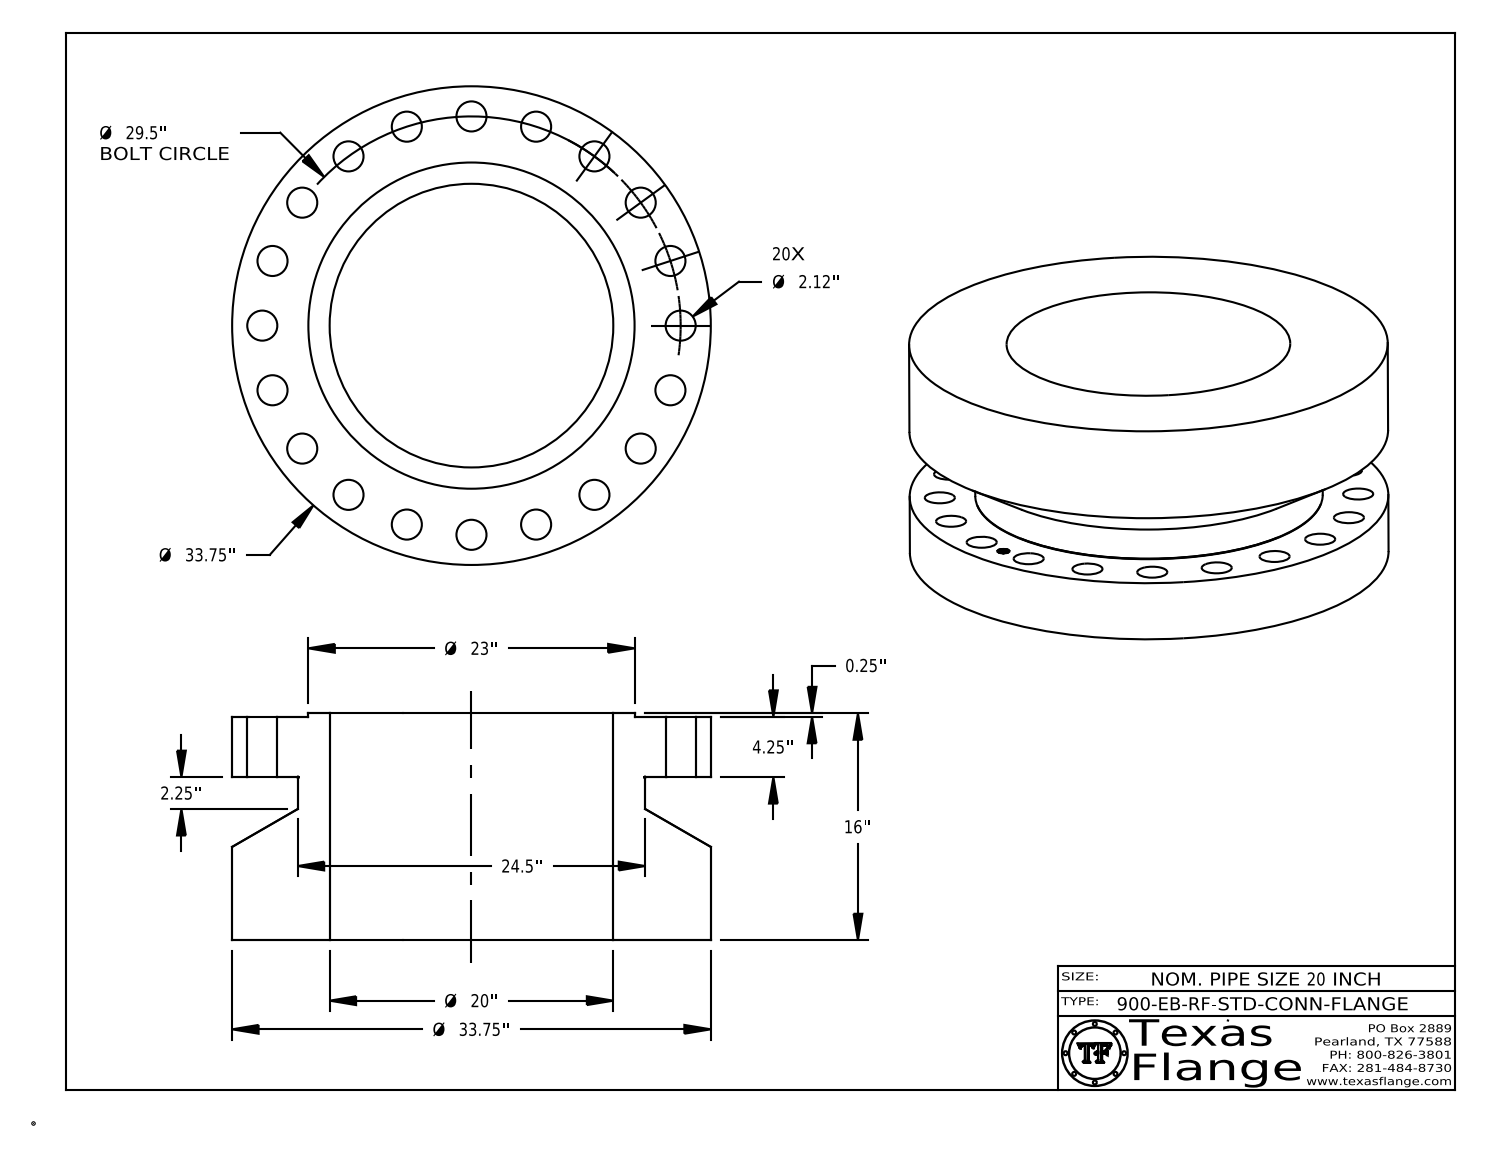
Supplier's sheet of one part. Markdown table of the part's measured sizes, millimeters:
| quantity | value |
| --- | --- |
| part name | 20-900-EB-RF-STD-CONN-FLANGE |
| STEP written by | CATIA V5 STEP AP214 (AUTOMOTIVE_DESIGN) |
| units | millimeters |
| bodies | 1 solid, 445 faces (369 planar, 70 cylindrical, 6 other) |
| overall size | 857.3 × 857.3 × 406.4 |
| volume | 120 000 000 mm³ |
| surface area | 3 126 000 mm² |
| round holes (diameter × count) | 53.8 × 20, 21.6 × 1, 508 × 1 |
| round bosses / shafts (diameter × count) | 1.3 × 8, 857.3 × 1, 622.3 × 1, 584.2 × 1, 17 × 1 |
| main face-to-face distances | 400.1, 108, 292.1, 6.4, 114.3, 406.4, 114.2, 107.8, 292.2, 6.5 |
| hole center spacings | 374.7, 740.1, 117.2, 440.4, 529.8, 606.2, 667.6, 231.5 |
